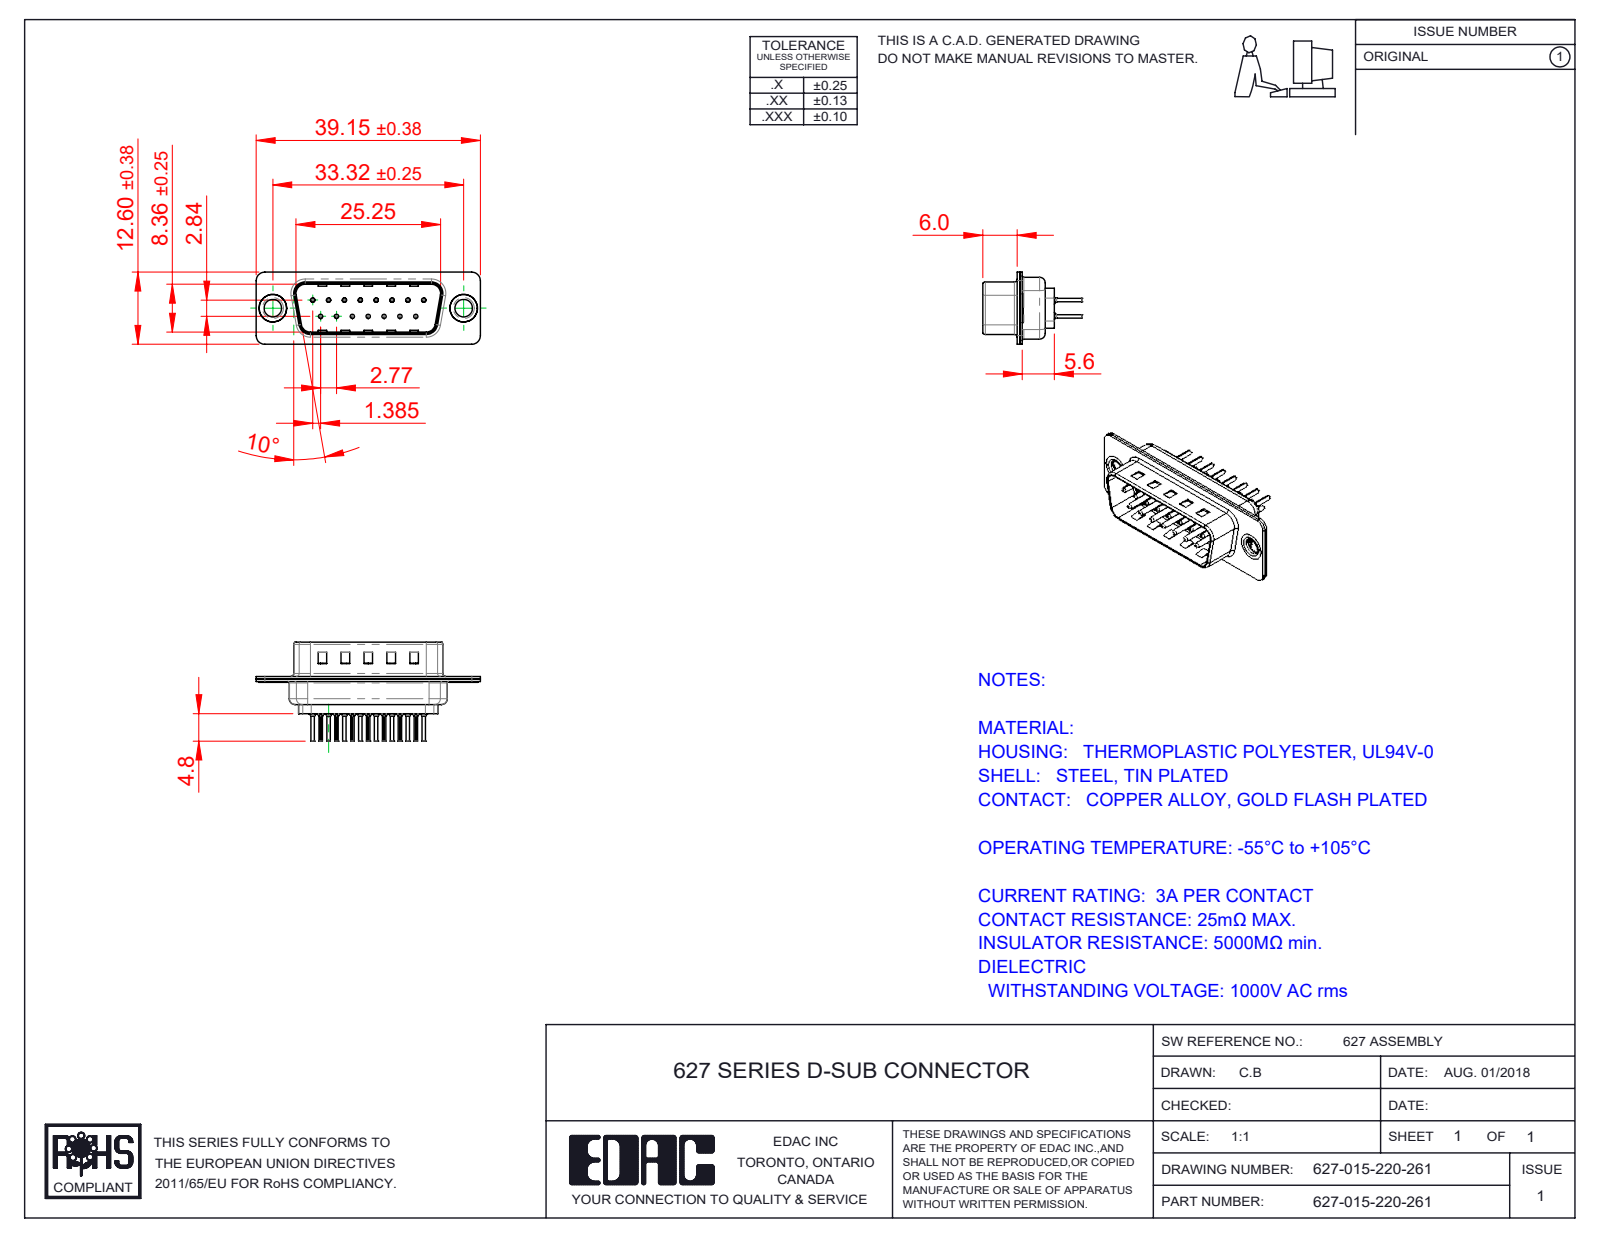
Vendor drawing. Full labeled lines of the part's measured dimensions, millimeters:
Part name (STEP PRODUCT): 627 Housing_15 LP; 627 Contact Row 1_20L; 627 Contact Row 2_20L; 627 Thru Hole Rivet (+3 more)
STEP written by: SolidWorks 2020 (CONFIG_CONTROL_DESIGN)
Units: millimetres
Bodies: 20 solids, 1784 faces (499 planar, 672 cylindrical, 613 other)
Overall size (bounding box): 39.15 × 17.3 × 12.6
Volume: 1 753 mm³ · Surface area: 5 247 mm²
Round holes (diameter × count): ⌀0.2 ×15, ⌀0.35 ×15, ⌀1.1 ×15, ⌀1.6 ×15, ⌀3.05 ×2, ⌀4 ×2, ⌀4.8 ×2
Round bosses / shafts (diameter × count): ⌀2 ×15, ⌀1.5 ×15, ⌀0.75 ×15, ⌀0.6 ×15, ⌀5 ×2, ⌀4.9 ×2, ⌀3.55 ×2
Partial cylindrical surfaces — rounded edges, fillets, slot ends (radius × count): R0.1 ×30, R1.5 ×16, R2 ×12, R0.5 ×8, R1.6 ×8, R0.25 ×4, R0.6 ×4, R0.65 ×4
Main face-to-face distances: 0.4, 0.45, 0.9, 0.82, 9.58, 8.76, 1.5, 1.4, 0.5, 6.5
Hole centre spacings: 3.16, 2.77, 5.54, 8.31, 11.08, 5.03, 5.04, 7.48
